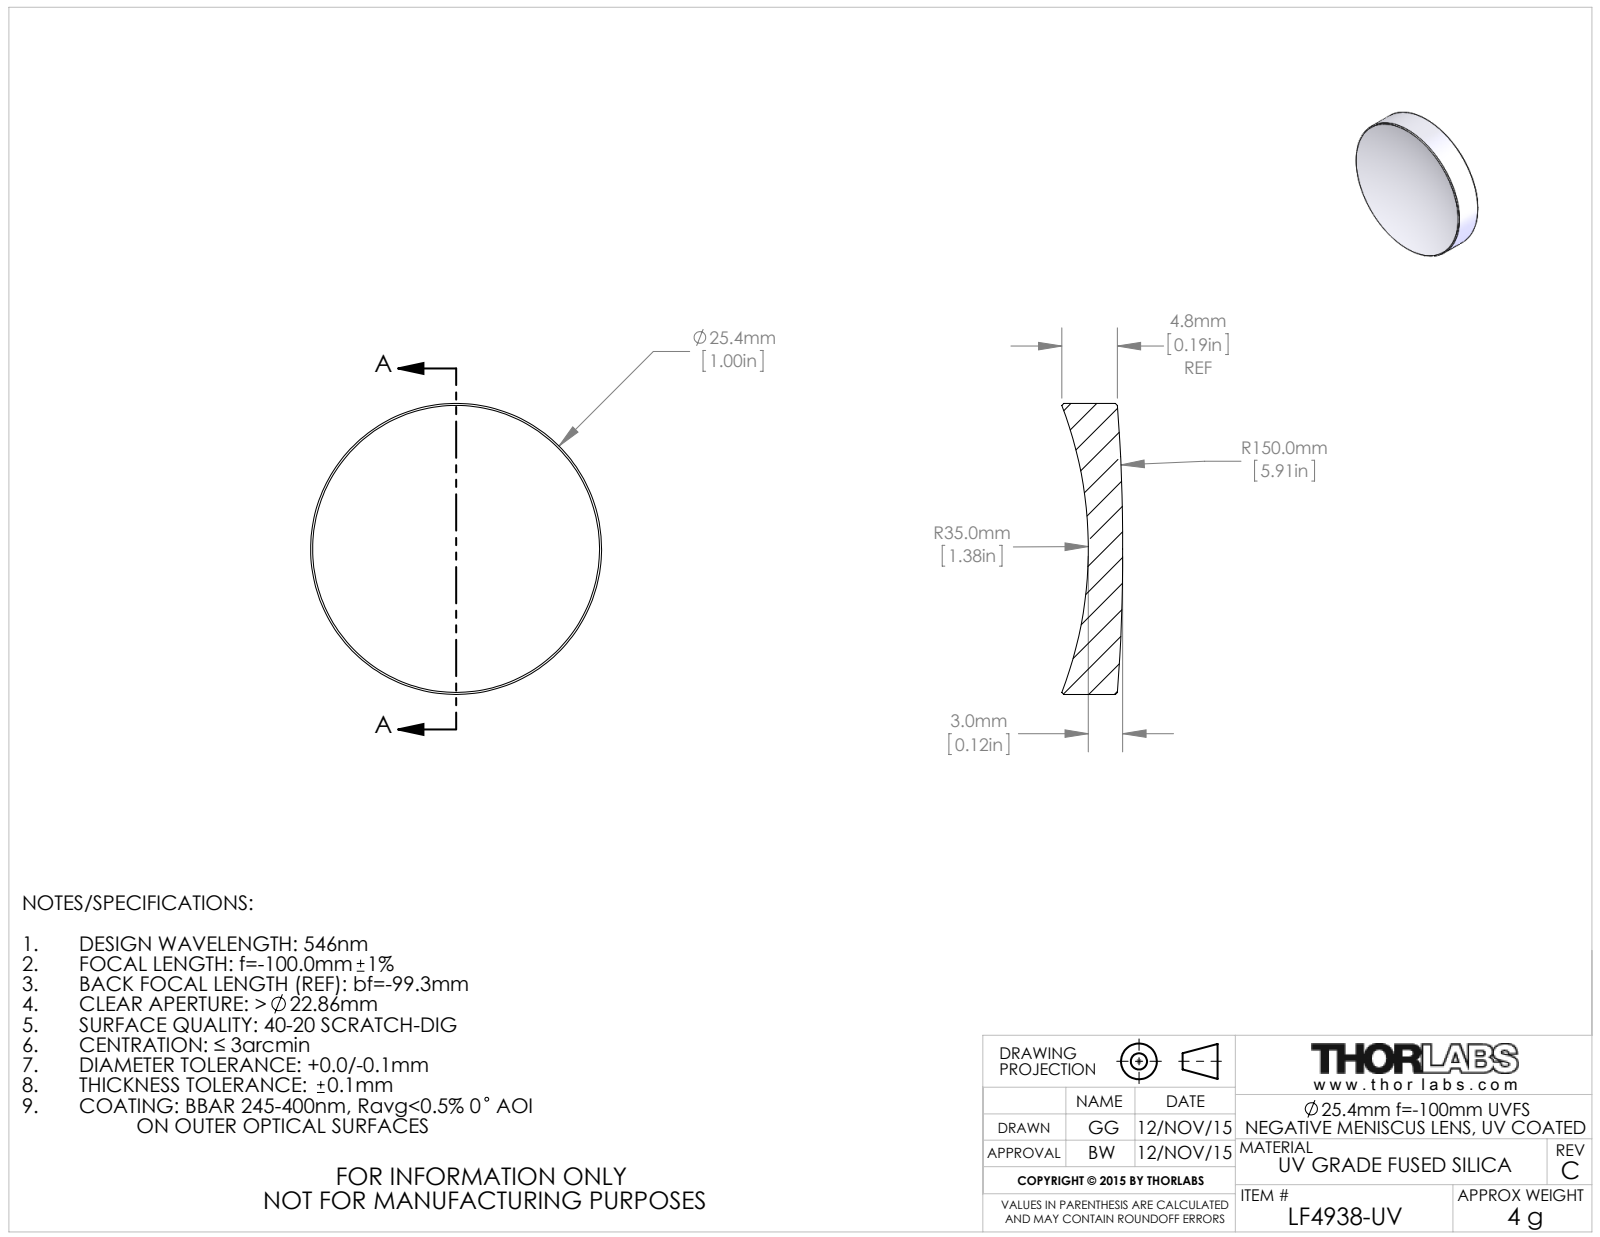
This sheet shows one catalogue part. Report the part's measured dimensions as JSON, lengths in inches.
{"part_name": "4937-E0W", "step_written_by": "SolidWorks 2014 (CONFIG_CONTROL_DESIGN)", "units": "inches", "bodies": {"solids": 1, "faces": 10, "planar": 0, "cylindrical": 2, "other": 8}, "overall_size": [1, 1, 0.209], "volume_in3": 0.122, "surface_area_in2": 2.172, "round_bosses_or_shafts": [[1, 1]]}
